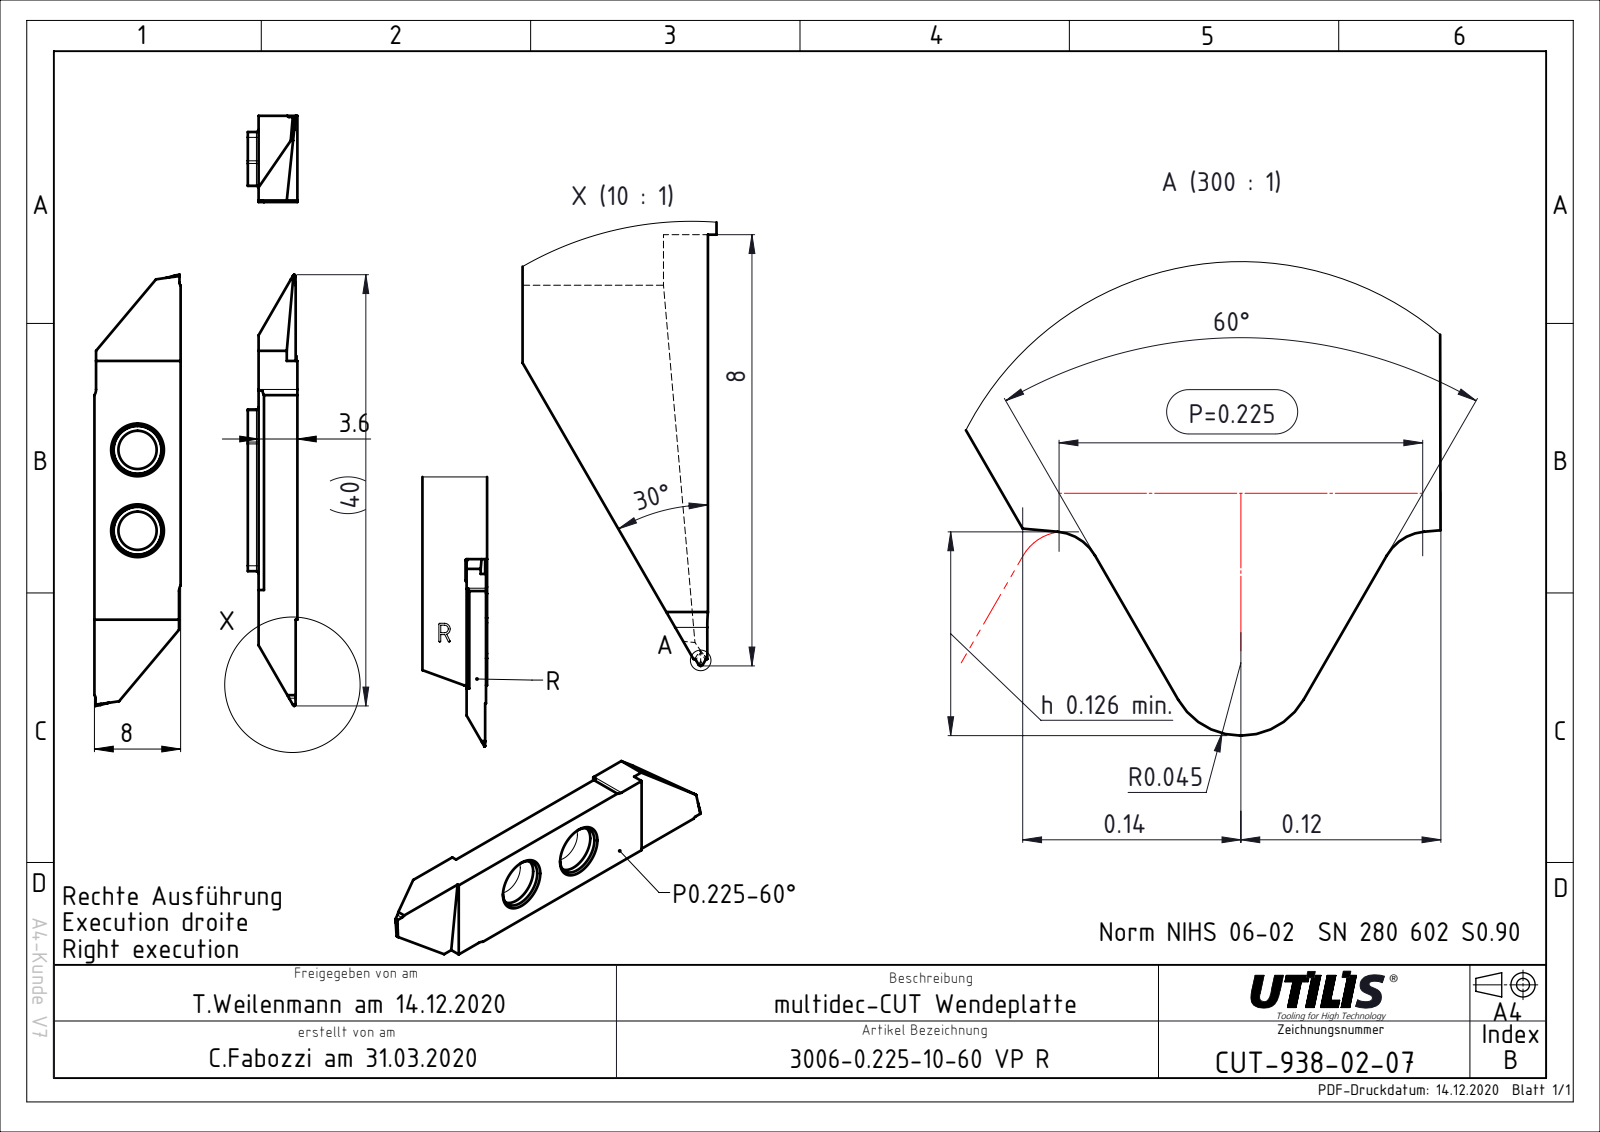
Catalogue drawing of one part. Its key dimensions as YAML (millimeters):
part_name: "CUT-938-02; ASME Y14.5"
step_written_by: "FormatWorks Professional (AP242_MANAGED_MODEL_BASED_3D_ENGINEERING_MIM_LF)"
units: millimeters
bodies: {solids: 1, faces: 46, planar: 30, cylindrical: 16, other: 0}
overall_size: [40, 8, 3.6]
volume: 810
surface_area: 841
round_holes:
  - {diameter: 3.55, count: 2}
partial_cylinders:
  - {radius: 1, count: 2}
face_to_face_distances: [3.6, 8, 7.85, 22.54, 7.7, 24, 4, 4.15, 11.85, 12]
hole_center_spacings: [7.5]
